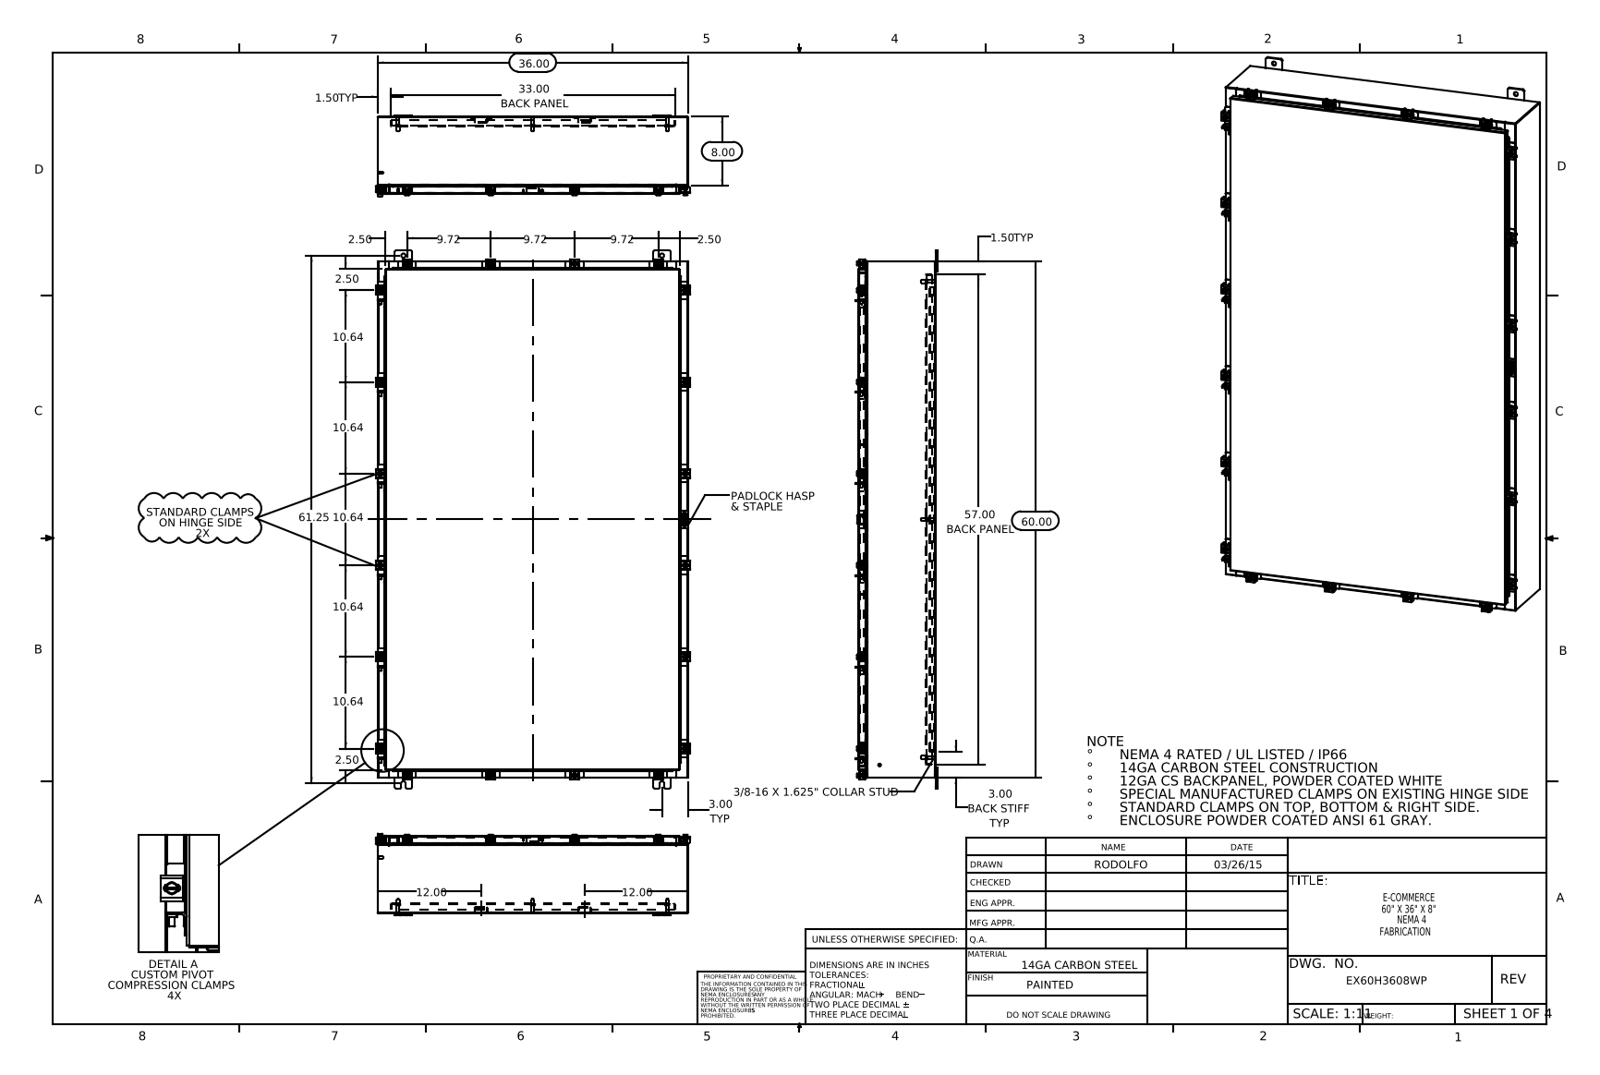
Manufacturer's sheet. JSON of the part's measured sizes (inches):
{"part_name": "EX60H3608WP Special Clamp; EX60H3608WP Clamp Assembly; HW-CLN-NH-20320; 22104005_DEFAULT_RTP30 (+8 more)", "step_written_by": "SolidWorks 2014 (CONFIG_CONTROL_DESIGN)", "units": "inches", "bodies": {"solids": 144, "faces": 3524, "planar": 1841, "cylindrical": 1347, "other": 336}, "overall_size": [62.5, 36.421, 9.453], "volume_in3": 736, "surface_area_in2": 18160, "round_holes": [[0.213, 20], [0.26, 20], [0.5, 12], [0.25, 9], [0.125, 1]], "round_bosses_or_shafts": [[0.5, 20], [0.25, 20], [0.399, 14], [0.625, 8], [0.375, 8], [0.33, 8], [0.157, 8], [0.14, 8]], "partial_cylinders_radius": [[0.06, 78], [0.141, 40], [0.013, 38], [0.09, 38], [0.088, 34], [0.12, 34], [0.05, 33], [0.145, 32]], "face_to_face_distances": [0.075, 8.9, 8.826, 8.975, 0.104, 1, 1.075, 7.826, 7.9, 1.179], "hole_center_spacings": [1.969, 2.224, 2.347, 13.972, 14.729, 16.126, 27.625, 29.744]}
